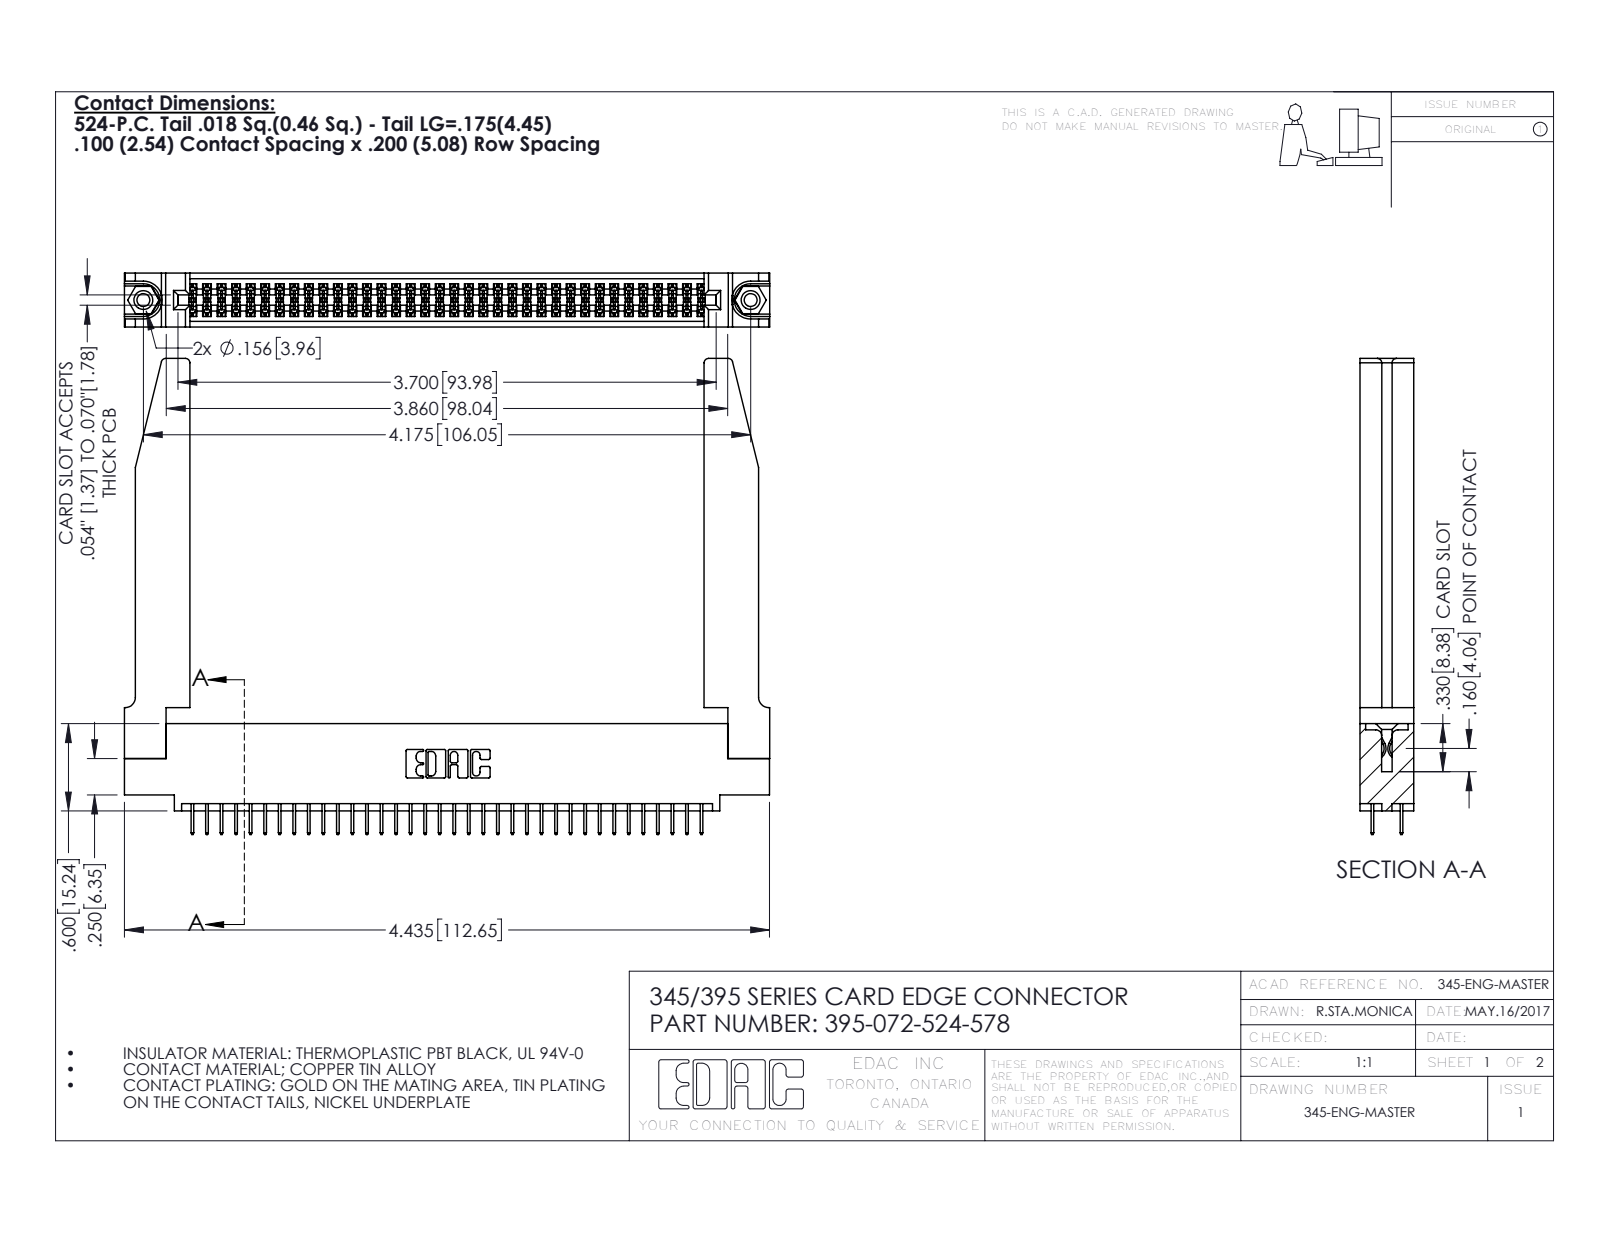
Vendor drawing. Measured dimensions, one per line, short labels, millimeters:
name: 345-220-078_345-220-078; 345-250-001_345-250-001-102; 345-292-001_345-293-124; 395-072-524-578 (+1 more)
written by: SolidWorks 2016 (CONFIG_CONTROL_DESIGN)
unit: mm
bodies: 77 solids, 4252 faces (3034 planar, 1166 cylindrical, 52 other)
size: 112.7 × 83.1 × 9.4
volume: 18 480 mm³; area: 22 350 mm²
holes: 2× ⌀2.3, 2× ⌀3.2, 2× ⌀4, 1× ⌀1.6
bosses: 2× ⌀3.9
rounds: 108× R0.2, 22× R0.3, 8× R0.8, 6× R0.2, 6× R0.8, 3× R0.7, 2× R0.4, 2× R0.5
face distances: 9.4, 1.8, 7.6, 5.1, 2.5, 6.9, 0.6, 5.7, 3.8, 3.8
hole spacings: 6.9, 100.1, 106
